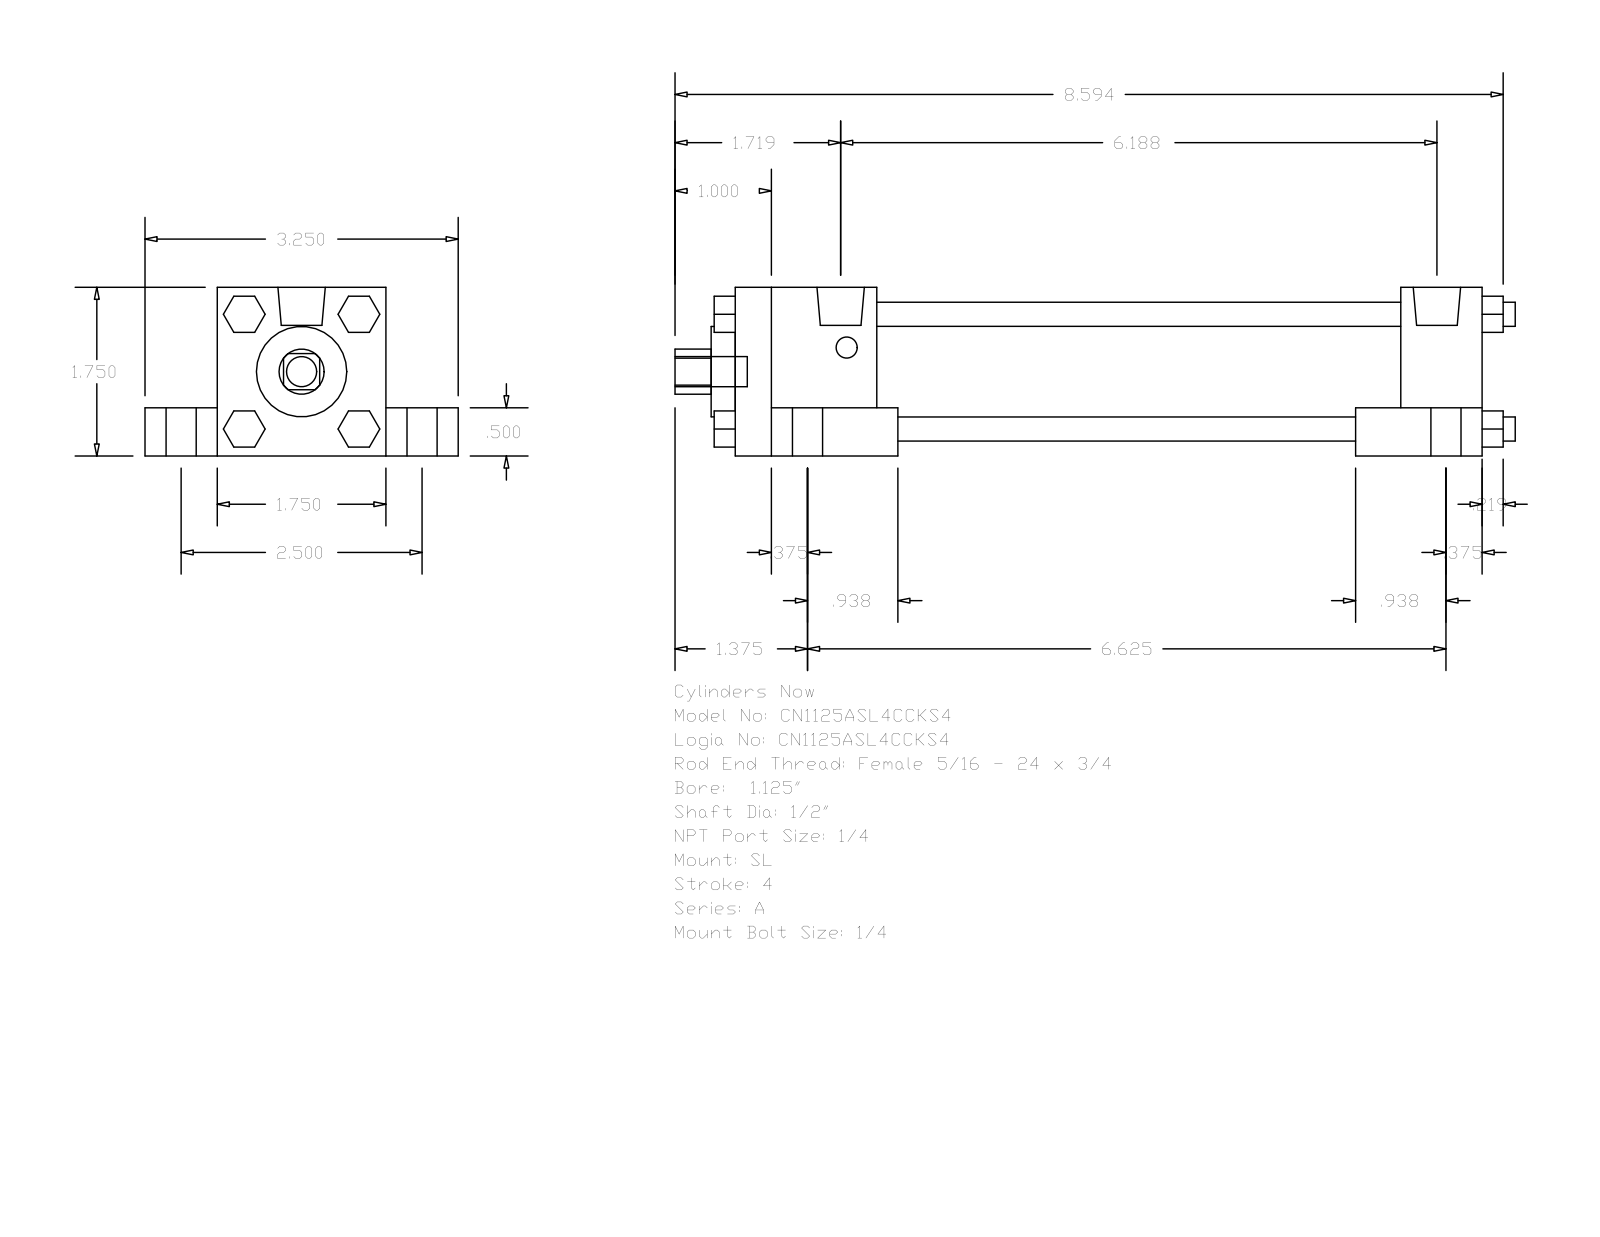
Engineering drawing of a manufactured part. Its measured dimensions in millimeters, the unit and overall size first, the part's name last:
Units: millimetres
Overall size (bounding box): 221.46 × 82.55 × 44.45
Round holes (diameter × count): ⌀12.7 ×1, ⌀23.81 ×1, ⌀31.88 ×1
Round bosses / shafts (diameter × count): ⌀7.94 ×5, ⌀14.29 ×4, ⌀6.35 ×4, ⌀5.56 ×4, ⌀12.49 ×2
Partial cylindrical surfaces — rounded edges, fillets, slot ends (radius × count): R5.94 ×1
Main face-to-face distances: 44.46, 31.76, 12.7, 19.04, 63.5, 159.54, 196.84, 175.41, 21.43, 37.3
Bodies: 0 solids, 150 faces (114 planar, 36 cylindrical, 0 other)
Part name (STEP PRODUCT): A_SL__0112_0.5
STEP written by: GSSL Pune (CONFIG_CONTROL_DESIGN)
